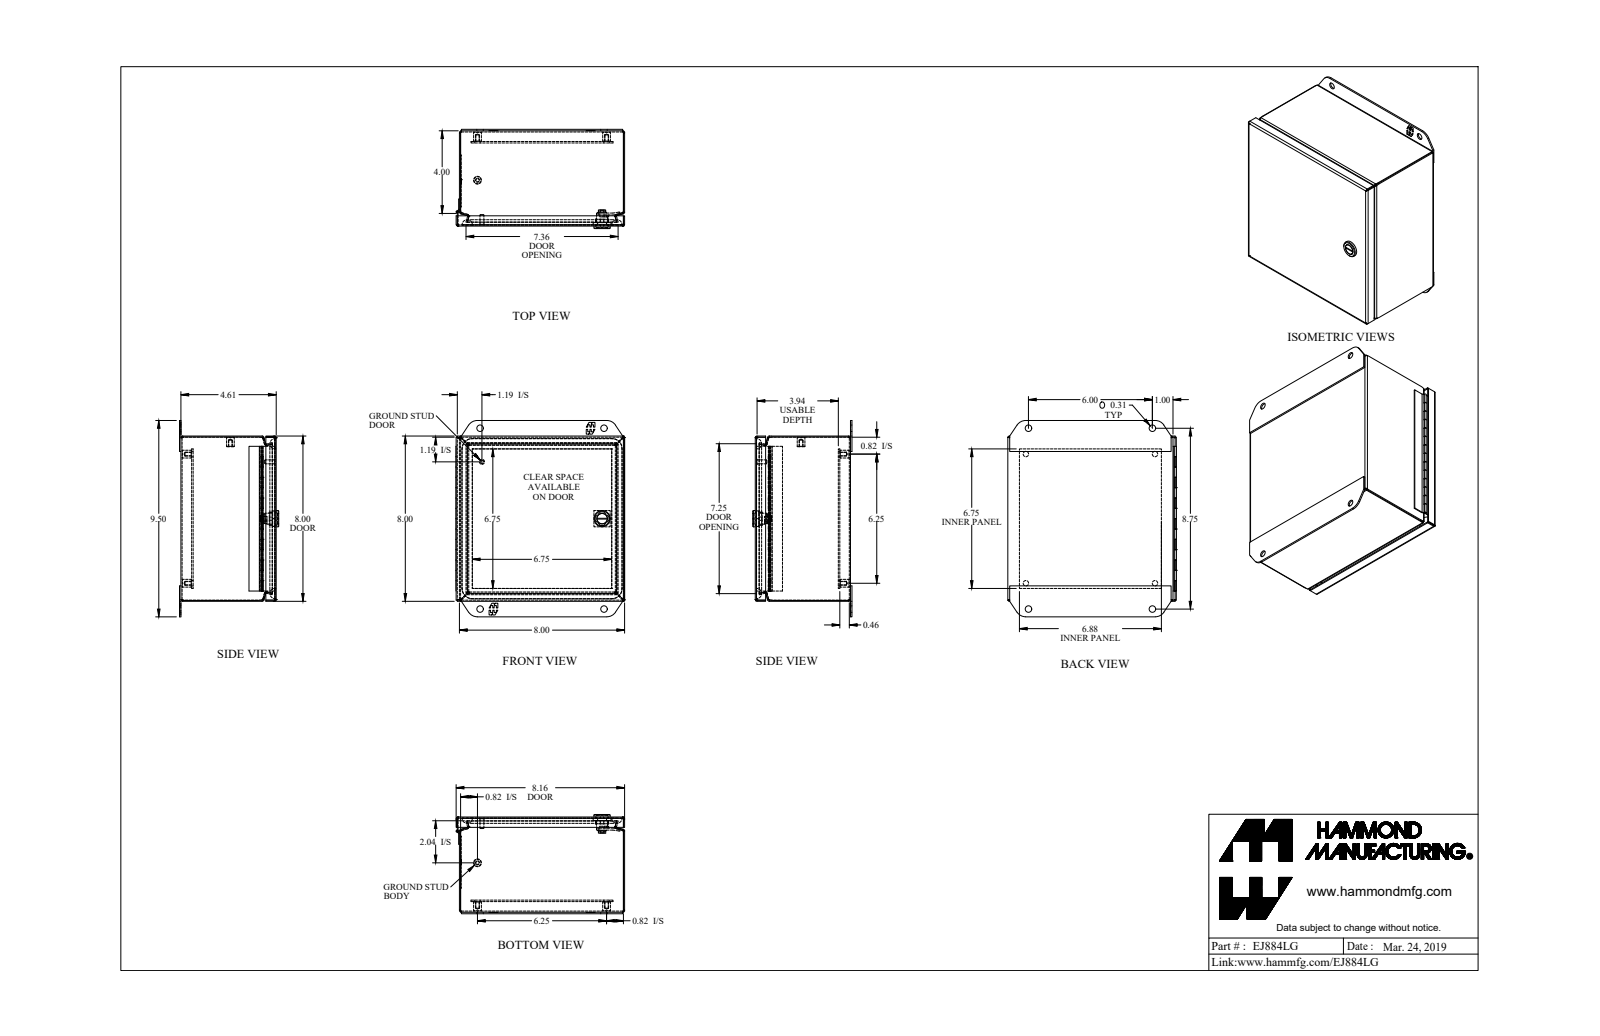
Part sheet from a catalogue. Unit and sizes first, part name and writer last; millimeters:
Units: millimetres
Overall size (bounding box): 241.3 × 207.4 × 122
Round holes (diameter × count): ⌀4 ×5, ⌀6.7 ×4, ⌀8 ×4, ⌀1.3 ×1, ⌀13.1 ×1
Round bosses / shafts (diameter × count): ⌀9.5 ×5, ⌀20 ×1, ⌀13.6 ×1, ⌀12.6 ×1, ⌀11 ×1, ⌀6.4 ×1, ⌀4.8 ×1, ⌀2.5 ×1
Partial cylindrical surfaces — rounded edges, fillets, slot ends (radius × count): R0.7 ×16, R2.2 ×16, R7.1 ×10, R6.4 ×4, R12.7 ×4, R12.7 ×4, R1.5 ×2, R13.7 ×2
Main face-to-face distances: 1.4, 115.7, 201.8, 1.8, 15, 203.2, 200.3, 117.1, 114.2, 11.7
Hole centre spacings: 31.9, 31.9, 79.6, 152.4, 158.8, 158.8, 158.8, 172.5
Volume: 408 400 mm³ · Surface area: 527 900 mm²
Bodies: 16 solids, 643 faces (361 planar, 190 cylindrical, 92 other)
Part name (STEP PRODUCT): EJ884LG_Default
STEP written by: SolidWorks 2019 (CONFIG_CONTROL_DESIGN)
